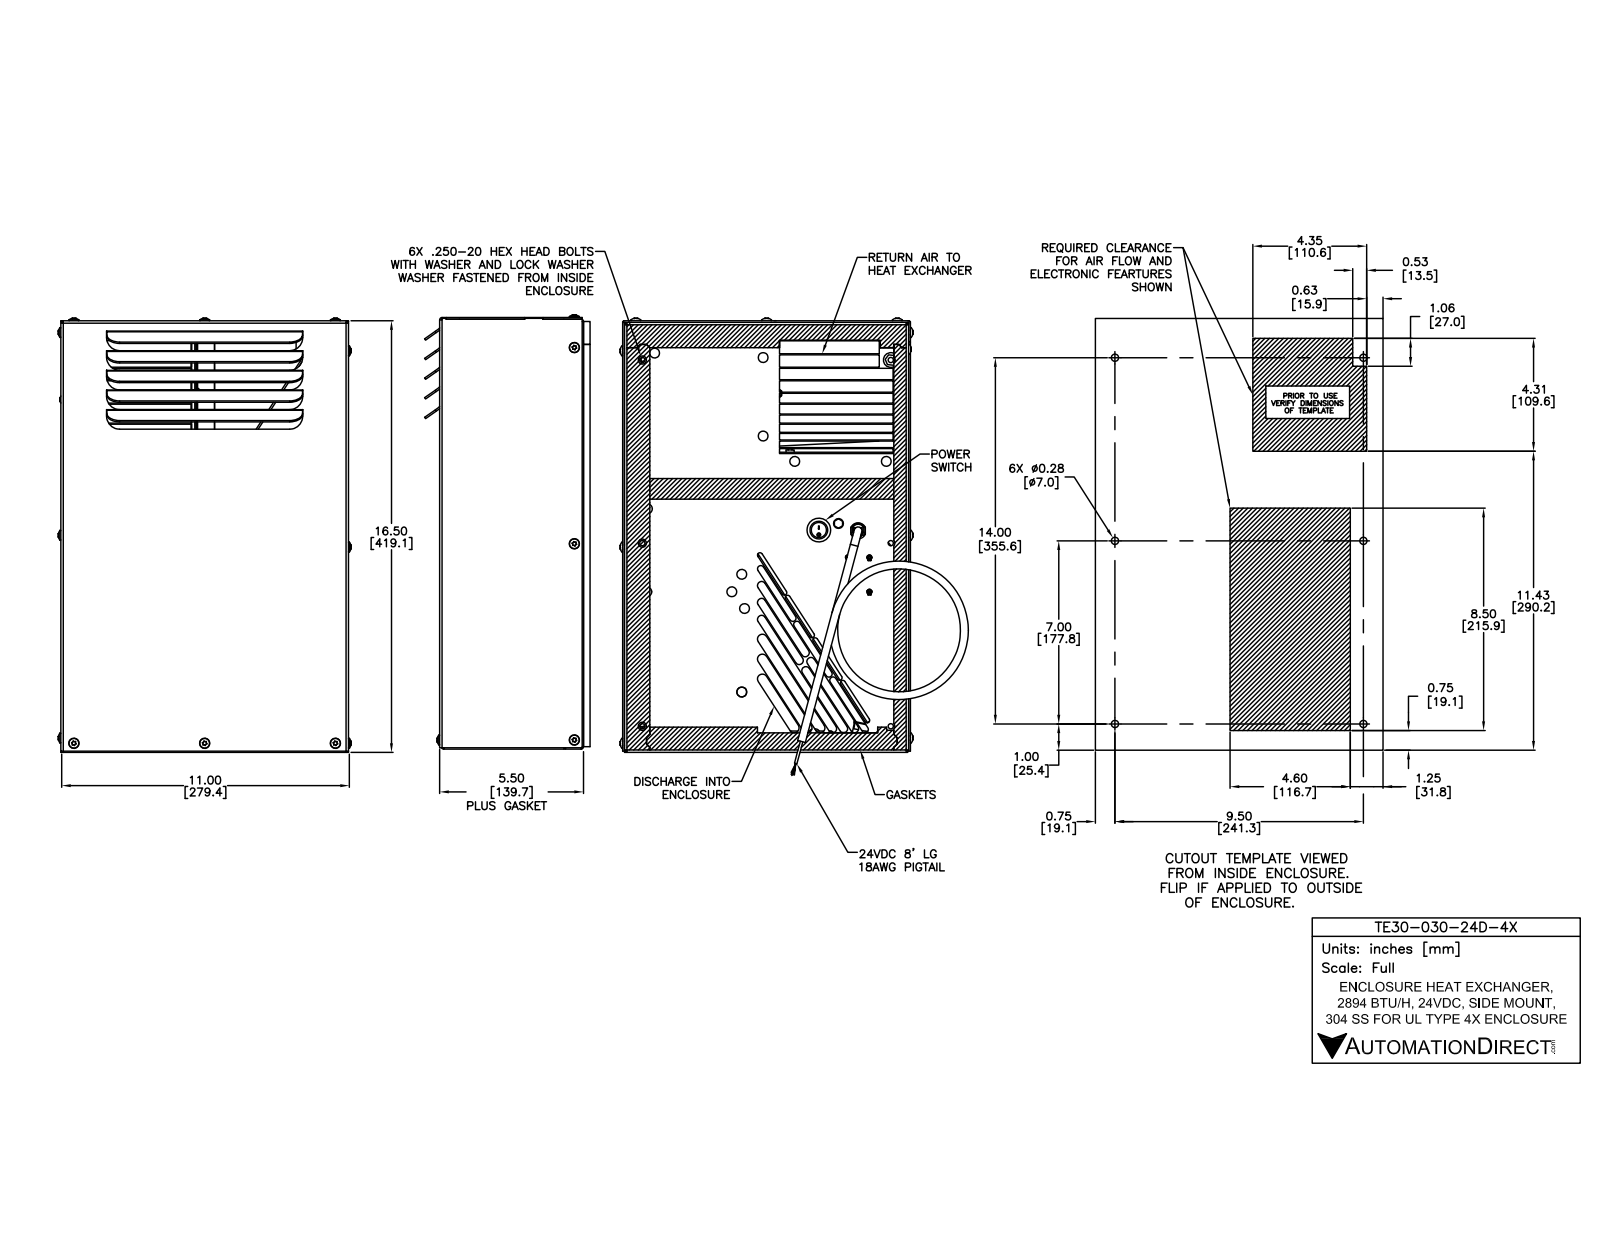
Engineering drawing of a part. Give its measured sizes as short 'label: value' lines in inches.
name: TE30-030-24D-4X
written by: SolidWorks 2017 (AUTOMOTIVE_DESIGN)
unit: in
bodies: 122 solids, 3166 faces (1807 planar, 975 cylindrical, 384 other)
size: 16.594 × 11.188 × 6.463
volume: 170.6 in³; area: 3 102 in²
holes: 23× ⌀0.188, 23× ⌀0.193, 19× ⌀0.219, 16× ⌀0.5, 9× ⌀0.203, 8× ⌀0.156, 7× ⌀0.109, 6× ⌀0.195, 6× ⌀0.2, 6× ⌀0.201, 6× ⌀0.25, 6× ⌀0.272
bosses: 23× ⌀0.27, 15× ⌀0.19, 6× ⌀0.564, 6× ⌀0.44, 6× ⌀0.344, 6× ⌀0.326, 6× ⌀0.325, 6× ⌀0.311
rounds: 84× R0.01, 84× R0.015, 59× R0.031, 46× R0.093, 18× R0.101, 17× R0.06, 13× R0.094, 12× R0.125
face distances: 0.062, 0.062, 10.871, 5.5, 5.376, 5.438, 5.438, 10.933, 10.809, 1.083
hole spacings: 1.25, 2.5, 3.75, 1.296, 1.205, 2.546, 0.06, 3.25
